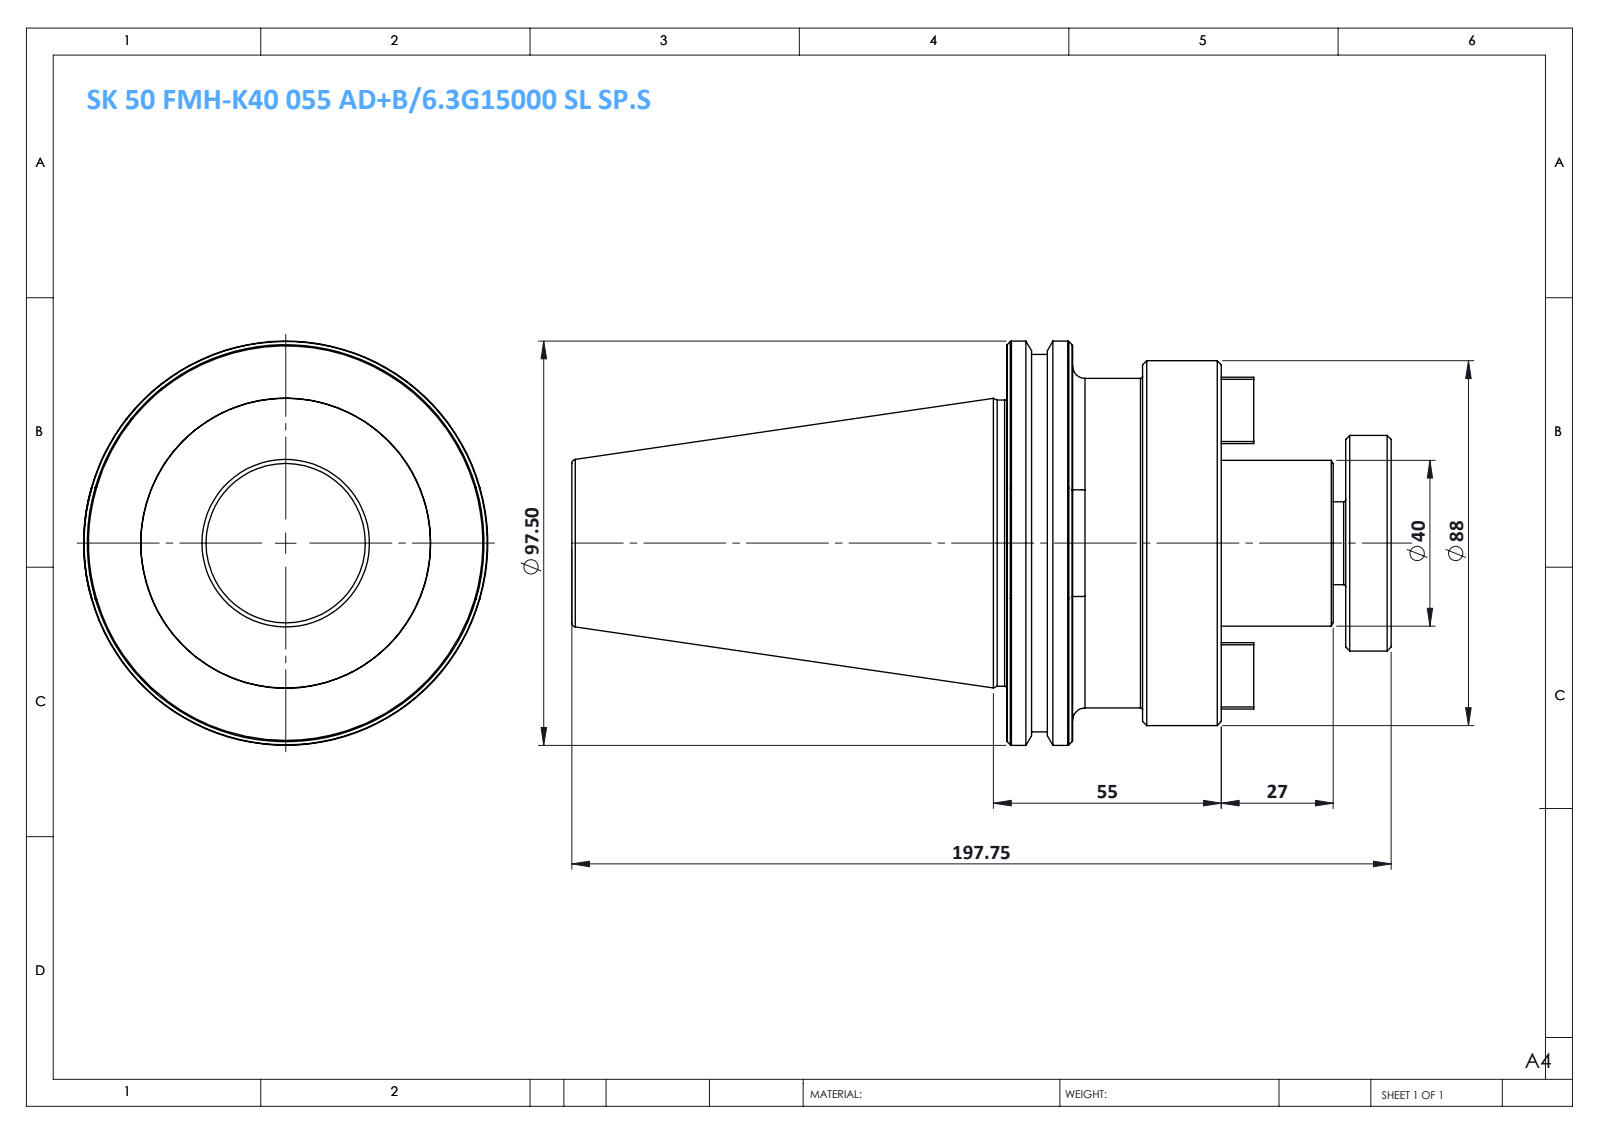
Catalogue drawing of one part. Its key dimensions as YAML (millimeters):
part_name: "SK50 FMH40 055 AD-6.3G15000 SL SP.S"
step_written_by: "SolidWorks 2014 (CONFIG_CONTROL_DESIGN)"
units: millimeters
bodies: {solids: 1, faces: 110, planar: 28, cylindrical: 18, other: 64}
overall_size: [197.75, 97.5, 97.5]
volume: 635227
surface_area: 57327
round_bosses_or_shafts:
  - {diameter: 97.5, count: 1}
  - {diameter: 91, count: 1}
  - {diameter: 88, count: 1}
  - {diameter: 79.5, count: 1}
  - {diameter: 69, count: 1}
  - {diameter: 52, count: 1}
  - {diameter: 40, count: 1}
  - {diameter: 20, count: 1}
face_to_face_distances: [51.8, 41, 92.8, 11, 30, 81.8, 76.9, 65.9, 35.9, 15.9]
